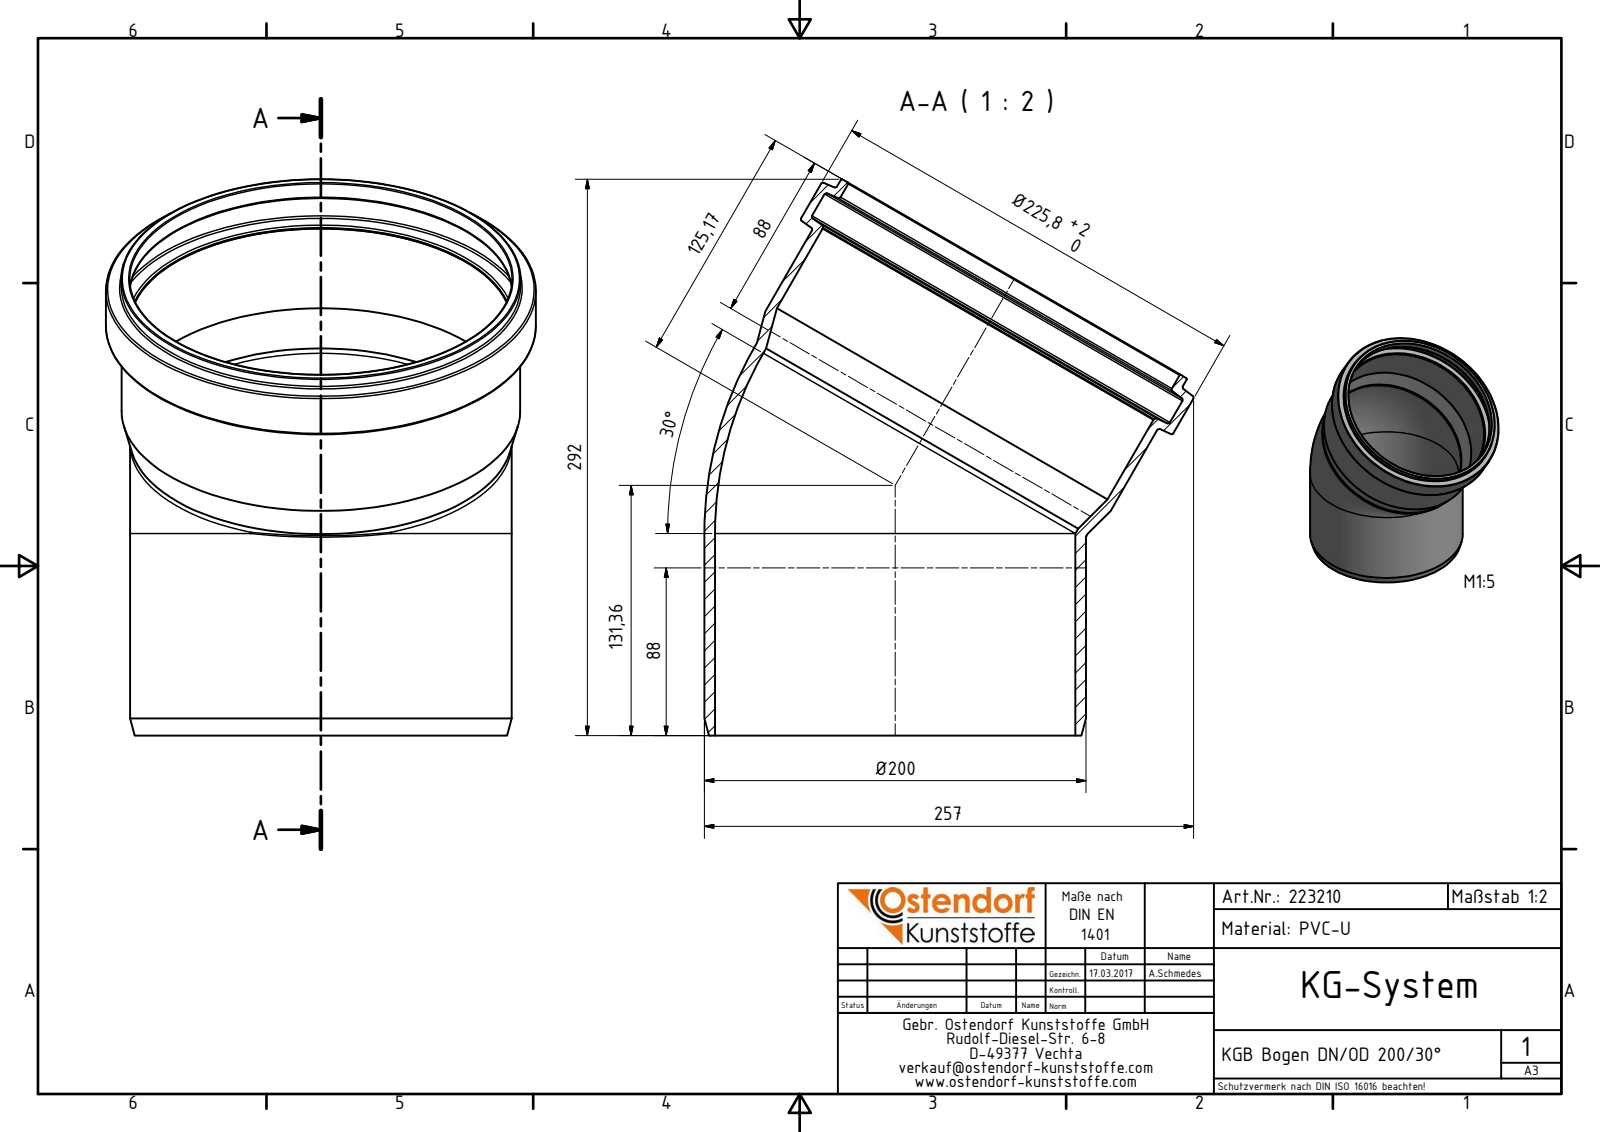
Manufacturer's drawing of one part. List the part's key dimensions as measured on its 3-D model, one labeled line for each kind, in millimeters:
Part name (STEP PRODUCT): 223210 KGB Bogen DN_OD 200_30°
STEP written by: Autodesk Inventor 2016 (AUTOMOTIVE_DESIGN)
Units: millimetres
Bodies: 1 solid, 34 faces (3 planar, 11 cylindrical, 20 other)
Overall size (bounding box): 292 × 257 × 225.8
Volume: 854 524 mm³ · Surface area: 343 721 mm²
Round holes (diameter × count): ⌀189.3 ×2, ⌀200.6 ×1, ⌀200.9 ×1, ⌀217 ×1
Round bosses / shafts (diameter × count): ⌀200.5 ×2, ⌀225.8 ×1, ⌀209.7 ×1, ⌀209.4 ×1
Main face-to-face distances: 27.56
